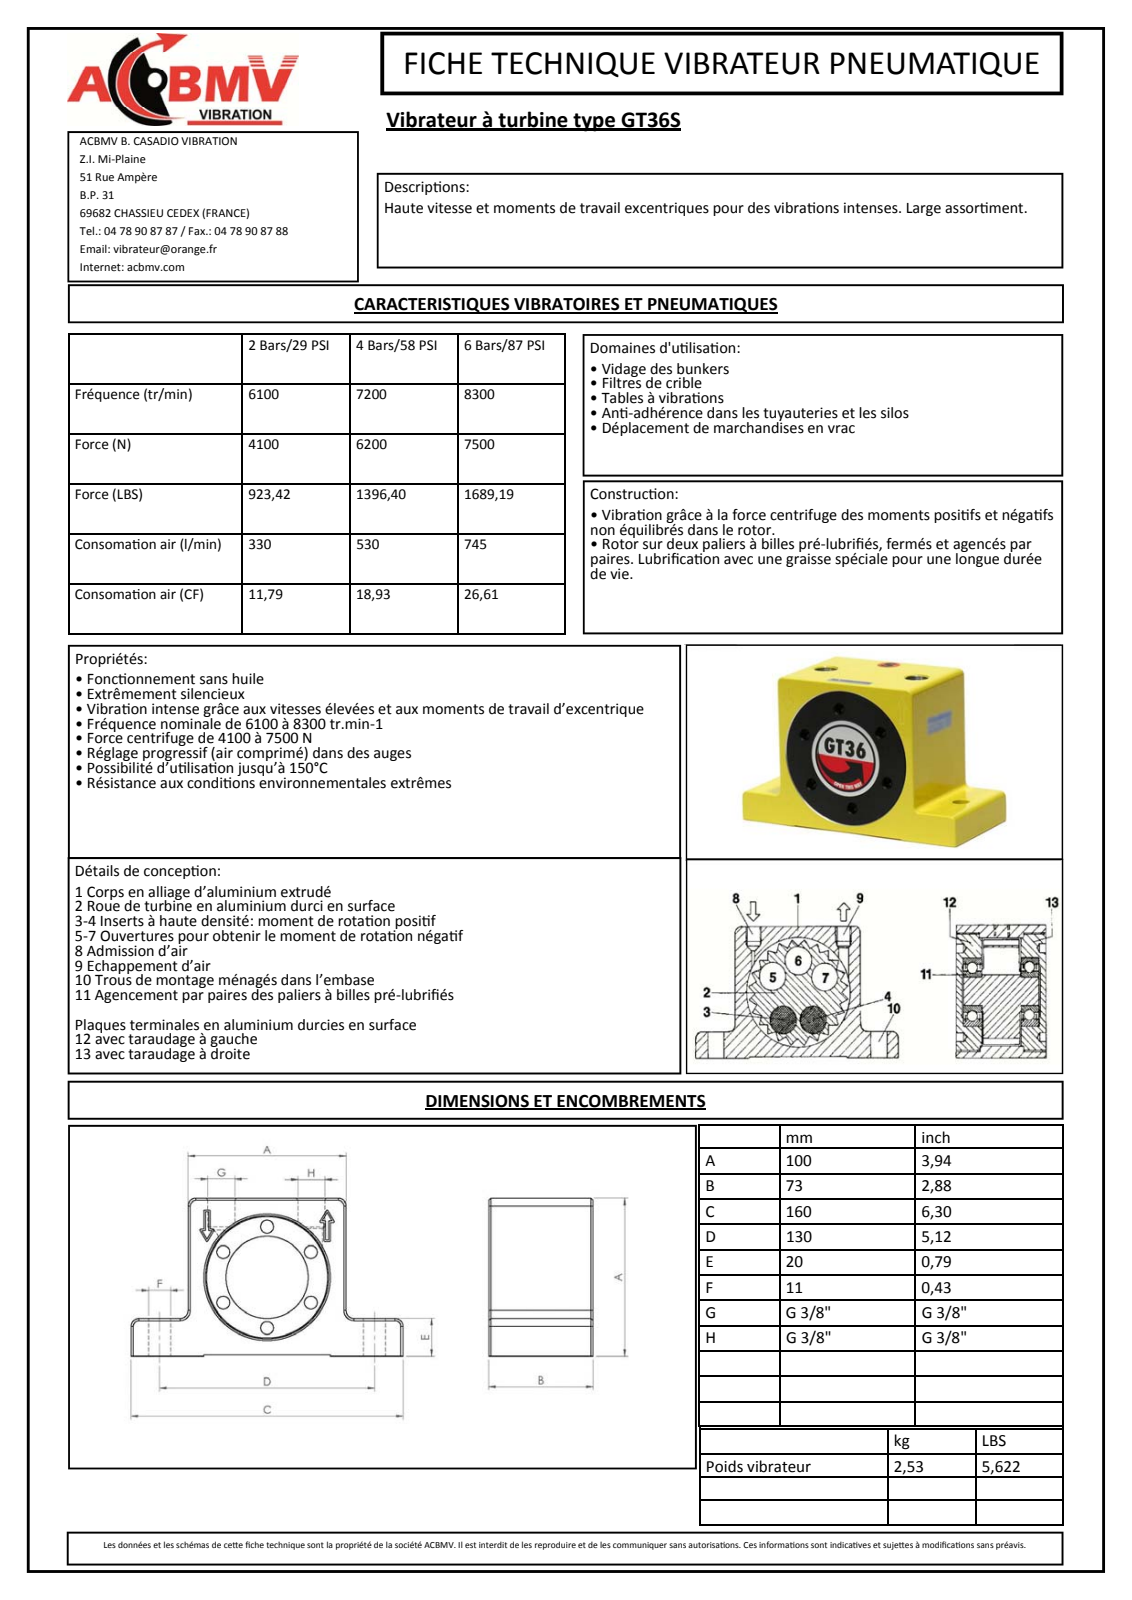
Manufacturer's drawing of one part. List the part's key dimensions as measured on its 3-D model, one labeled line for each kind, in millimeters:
Part name (STEP PRODUCT): 8036-10-M
STEP written by: Autodesk Inventor 2011 (CONFIG_CONTROL_DESIGN)
Units: millimetres
Bodies: 1 solid, 275 faces (172 planar, 73 cylindrical, 30 other)
Overall size (bounding box): 160 × 100 × 73
Volume: 781 808 mm³ · Surface area: 68 469 mm²
Round holes (diameter × count): ⌀7 ×6, ⌀11 ×4, ⌀14.95 ×2, ⌀2.98 ×1, ⌀51 ×1
Round bosses / shafts (diameter × count): ⌀2.68 ×1
Partial cylindrical surfaces — rounded edges, fillets, slot ends (radius × count): R0.3 ×14, R4 ×6, R0.77 ×4, R0.9 ×3, R1.03 ×3, R2.06 ×3, R0.39 ×2, R0.52 ×2
Main face-to-face distances: 100, 0.5, 72.7, 99.5, 73, 0.8, 72.2, 71.9, 72.4, 80
Hole centre spacings: 33, 57.16, 66, 24.34, 31, 40.31, 55.17, 55.68
